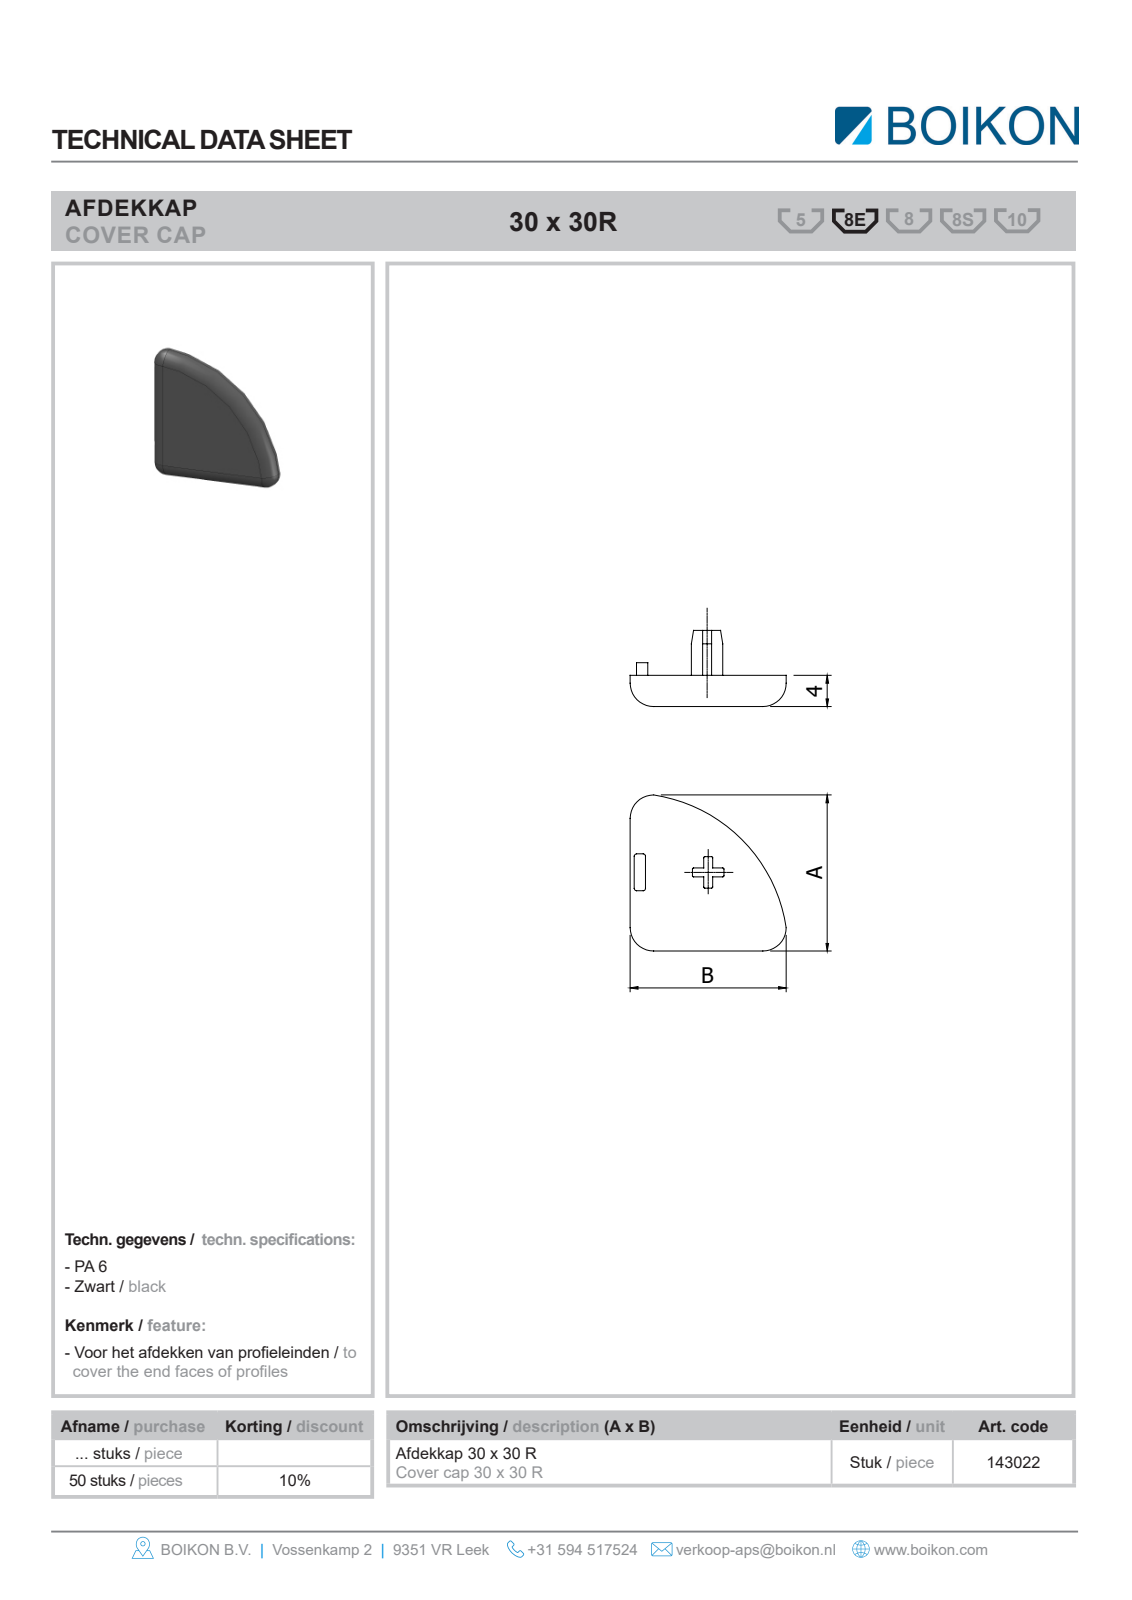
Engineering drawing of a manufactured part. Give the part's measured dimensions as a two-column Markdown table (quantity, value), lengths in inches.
| quantity | value |
| --- | --- |
| part name | Root; 143022 Afdekkap 30 x 30-RBOIKON |
| STEP written by | HiCAD 2013 1802.4 Build 509 (AUTOMOTIVE_DESIGN) |
| units | inches |
| bodies | 1 solid, 18 faces (6 planar, 8 cylindrical, 4 other) |
| overall size | 1.181 × 1.181 × 0.157 |
| volume | 0.174 in³ |
| surface area | 2.793 in² |
| partial cylindrical surfaces (radius × count) | 0.118 × 7, 0.984 × 1 |
| main face-to-face distances | 0.157, 1.181 |
